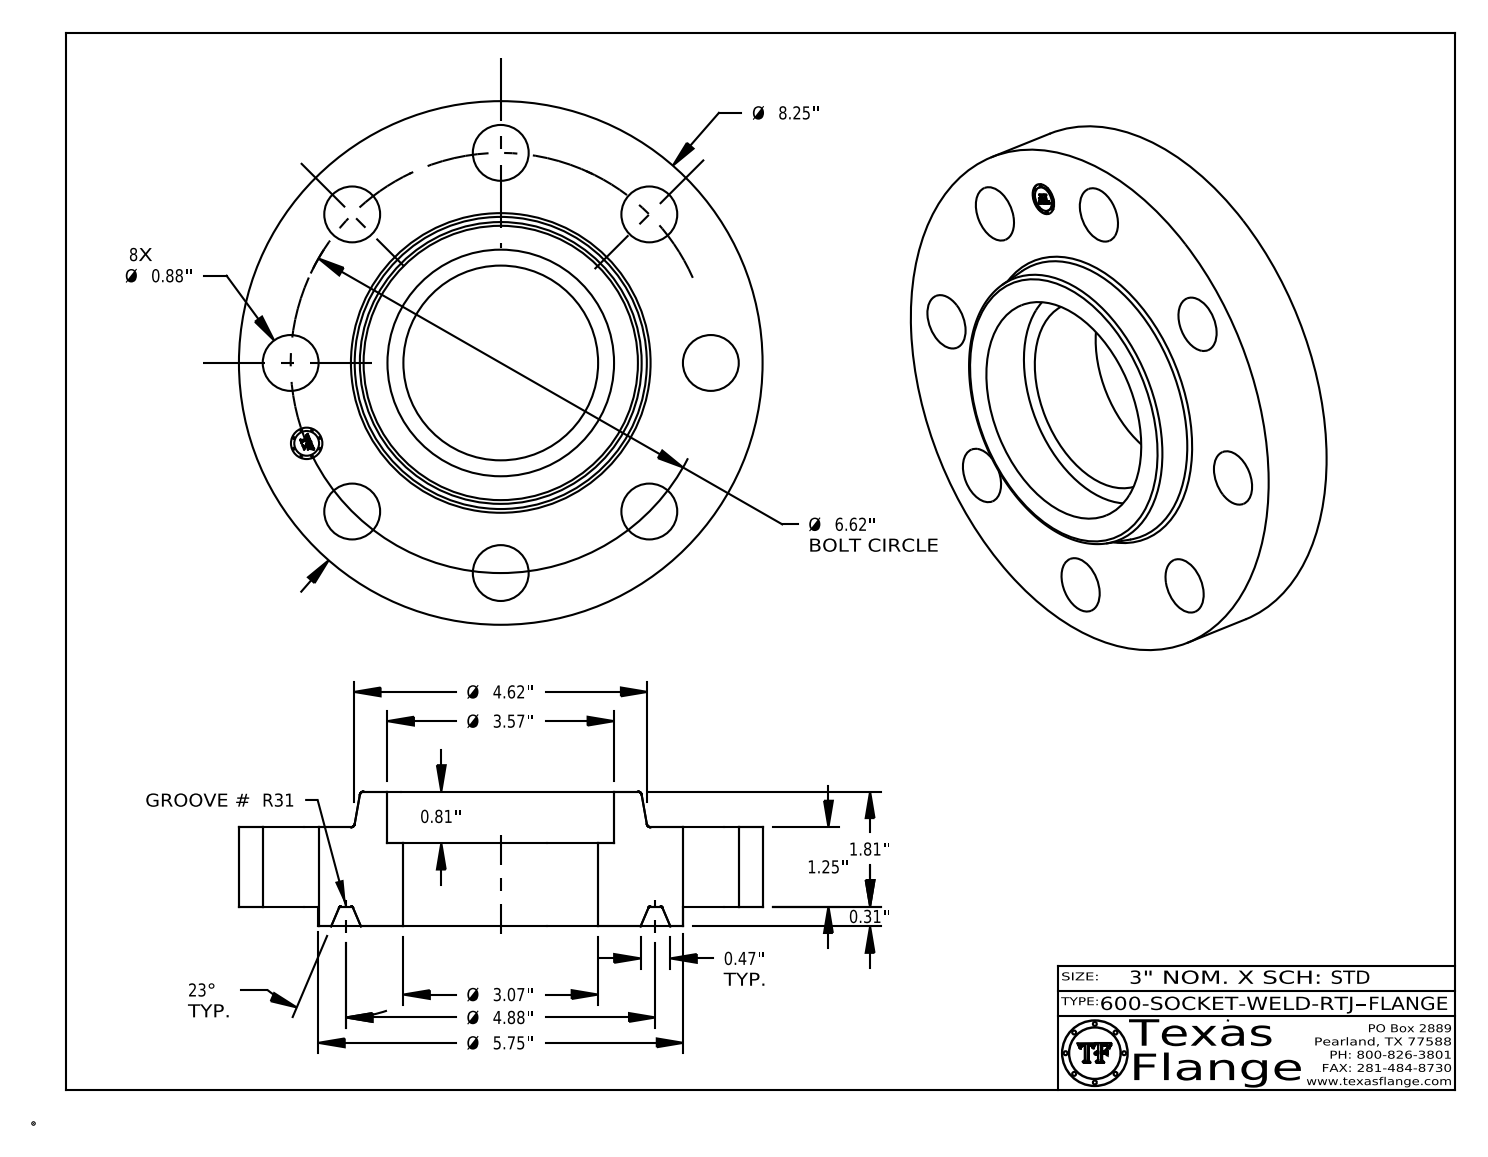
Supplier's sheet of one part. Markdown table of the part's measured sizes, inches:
| quantity | value |
| --- | --- |
| part name | 600-SOCKET-WELD-RTJ |
| STEP written by | CATIA V5 STEP AP214 (AUTOMOTIVE_DESIGN) |
| units | inches |
| bodies | 1 solid, 438 faces (372 planar, 52 cylindrical, 14 other) |
| overall size | 8.25 × 8.25 × 2.123 |
| volume | 58.43 in³ |
| surface area | 182.3 in² |
| round holes (diameter × count) | 0.88 × 8, 0.495 × 1, 3.068 × 1, 3.57 × 1 |
| round bosses / shafts (diameter × count) | 0.03 × 8, 8.25 × 1, 5.75 × 1, 0.39 × 1 |
| main face-to-face distances | 1.25, 0.313, 1.563, 2.123, 1.81, 0.56, 1.313, 1, 0.25, 0.81 |
| hole center spacings | 3.31, 2.533, 6.116, 4.681, 4.681, 1.291, 3.678, 6.493 |
